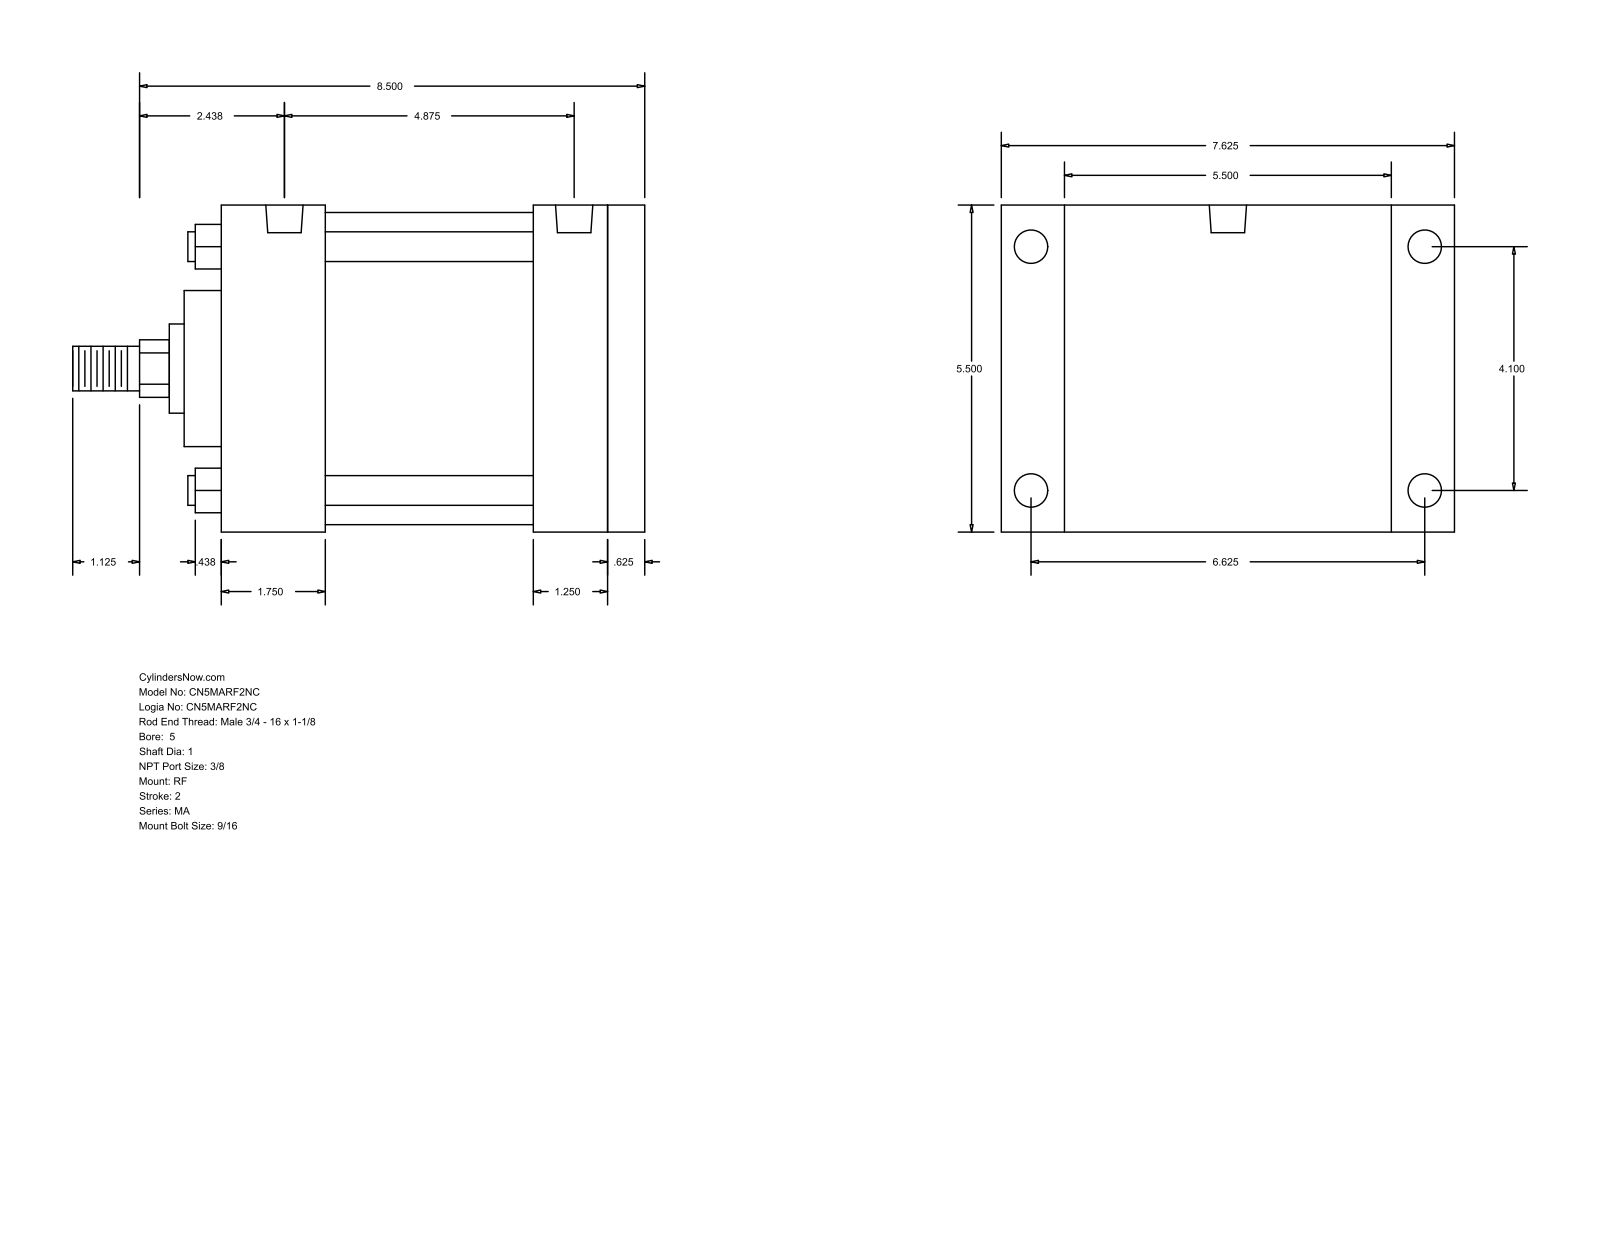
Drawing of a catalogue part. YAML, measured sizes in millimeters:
part_name: "MA_RF__0500_1"
step_written_by: "GSSL Pune (CONFIG_CONTROL_DESIGN)"
units: millimeters
bodies: {solids: 0, faces: 94, planar: 65, cylindrical: 29, other: 0}
overall_size: [244.47, 193.68, 139.7]
round_holes:
  - {diameter: 11.11, count: 4}
  - {diameter: 14.29, count: 4}
  - {diameter: 15.93, count: 2}
round_bosses_or_shafts:
  - {diameter: 12.7, count: 4}
  - {diameter: 133.35, count: 1}
  - {diameter: 66.67, count: 1}
  - {diameter: 38.1, count: 1}
  - {diameter: 25.4, count: 1}
  - {diameter: 19.05, count: 1}
partial_cylinders:
  - {radius: 12.29, count: 1}
face_to_face_distances: [139.7, 180.98, 15.87, 165.11, 47.62, 44.46, 120.65, 136.52, 133.36, 88.9]
hole_center_spacings: [104.14, 114.3, 168.28, 197.9, 4.76, 4.77, 119.06, 119.07]
